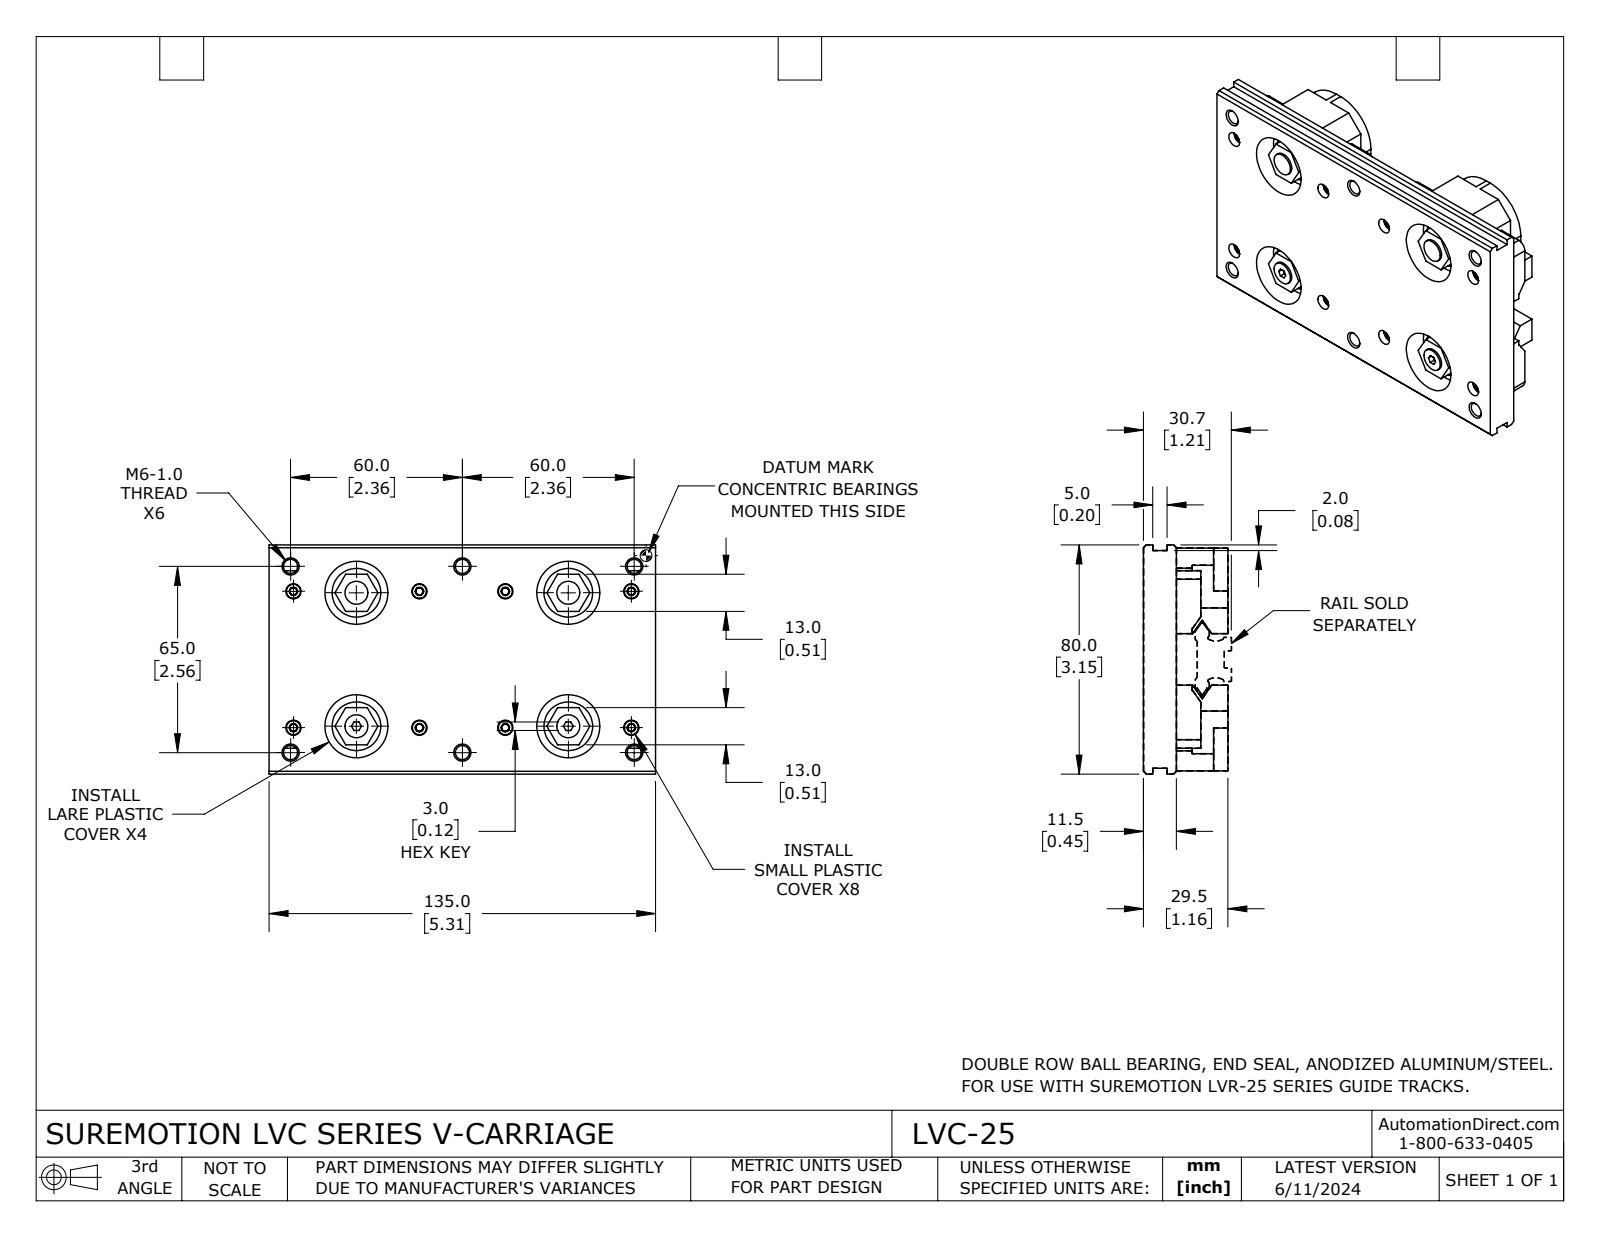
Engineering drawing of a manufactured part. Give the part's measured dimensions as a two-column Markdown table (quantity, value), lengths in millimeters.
| quantity | value |
| --- | --- |
| part name | LVC-25 |
| STEP written by | SolidWorks 2023 (CONFIG_CONTROL_DESIGN) |
| units | millimeters |
| bodies | 17 solids, 760 faces (396 planar, 180 cylindrical, 184 other) |
| overall size | 135 × 80 × 29.5 |
| volume | 221 099 mm³ |
| surface area | 68 428 mm² |
| round holes (diameter × count) | 3.5 × 8, 5.3 × 8, 2.01 × 4, 2.01 × 4, 4.92 × 4, 22 × 4, 4.92 × 2 |
| round bosses / shafts (diameter × count) | 5.5 × 8, 3 × 8, 25 × 4, 17 × 4, 10 × 4, 8 × 4 |
| partial cylindrical surfaces (radius × count) | 3 × 16, 15 × 8 |
| main face-to-face distances | 11.5, 18, 2, 29.5, 16, 49, 3.1, 21.1, 8.4, 20 |
| hole center spacings | 22.01, 51.98, 74, 8.76, 17.34, 24.77, 38.13, 44 |
